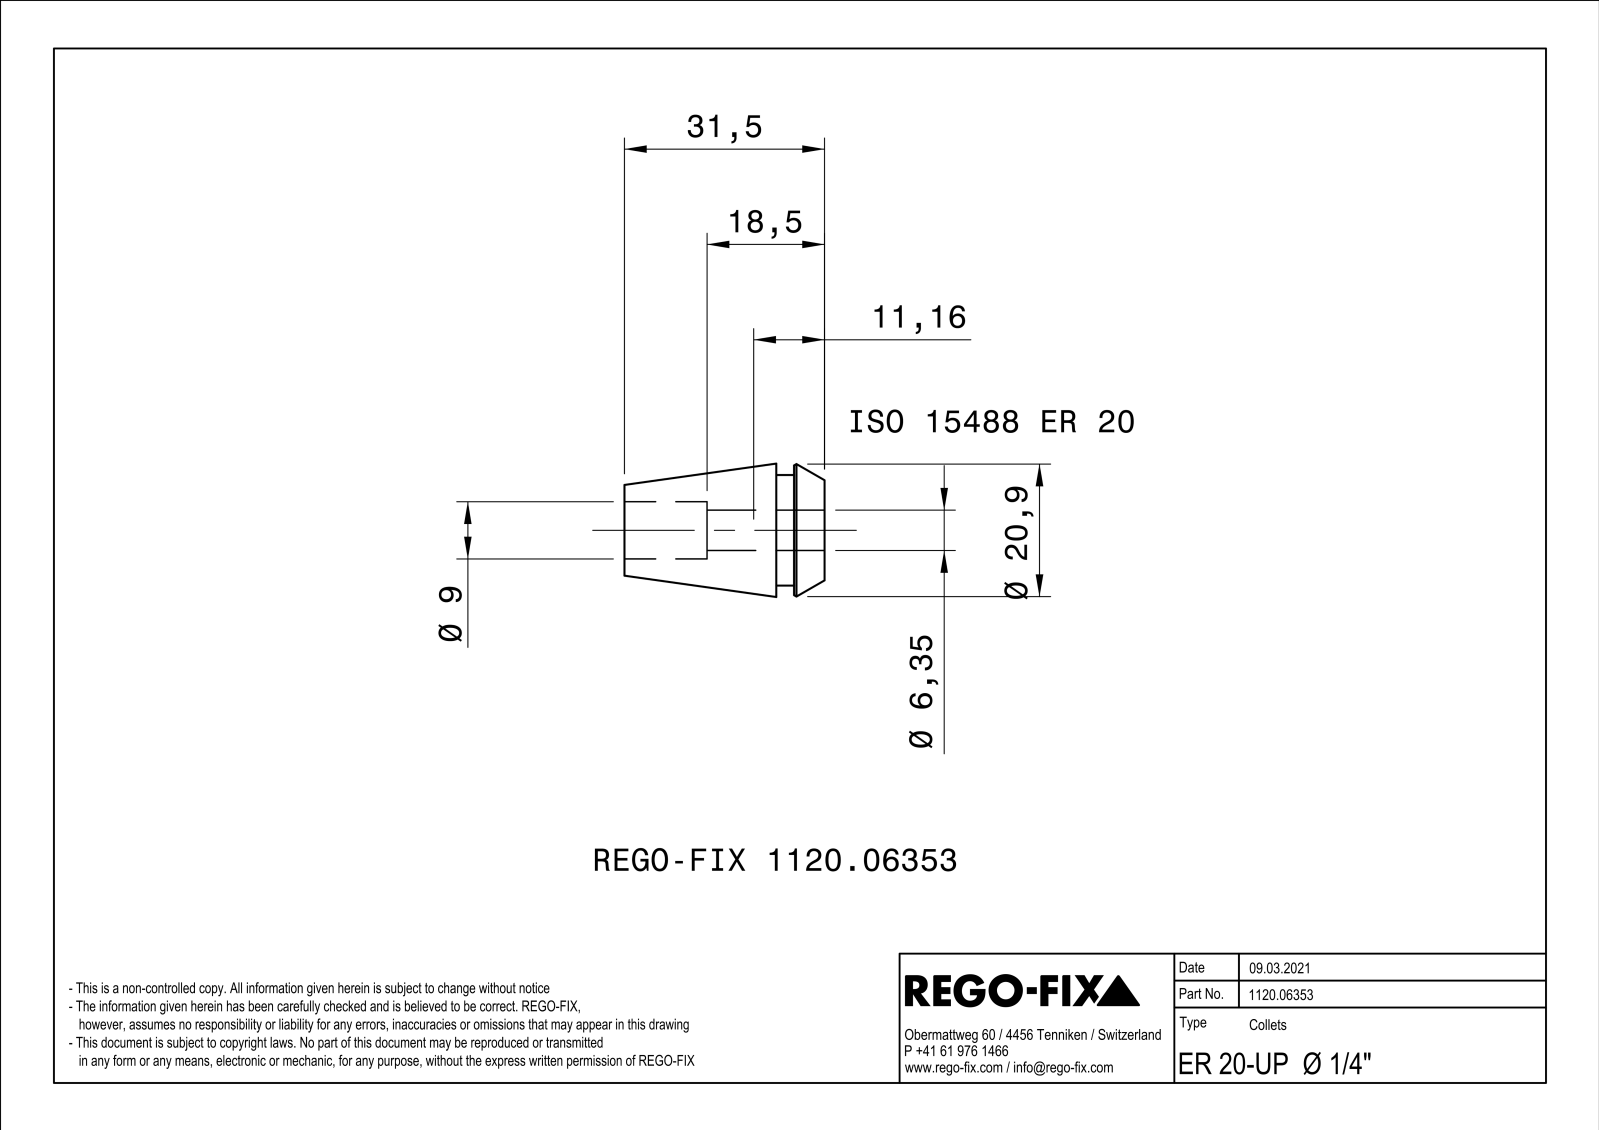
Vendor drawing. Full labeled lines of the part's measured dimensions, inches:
Part name (STEP PRODUCT): NOCUT
STEP written by: SIEMENS PLM Software Solid Edge ST10 (AUTOMOTIVE_DESIGN)
Units: inches
Bodies: 1 solid, 257 faces (104 planar, 41 cylindrical, 112 other)
Overall size (bounding box): 1.24 × 0.826 × 0.826
Volume: 0.324 in³ · Surface area: 9.914 in²
Round holes (diameter × count): ⌀0.354 ×1
Round bosses / shafts (diameter × count): ⌀0.685 ×1
Partial cylindrical surfaces — rounded edges, fillets, slot ends (radius × count): R1.575 ×8, R0.125 ×1
Main face-to-face distances: 0.024, 0.024, 0.023, 0.299, 0.189, 0.11, 1.24, 1.051, 0.941, 1.063
